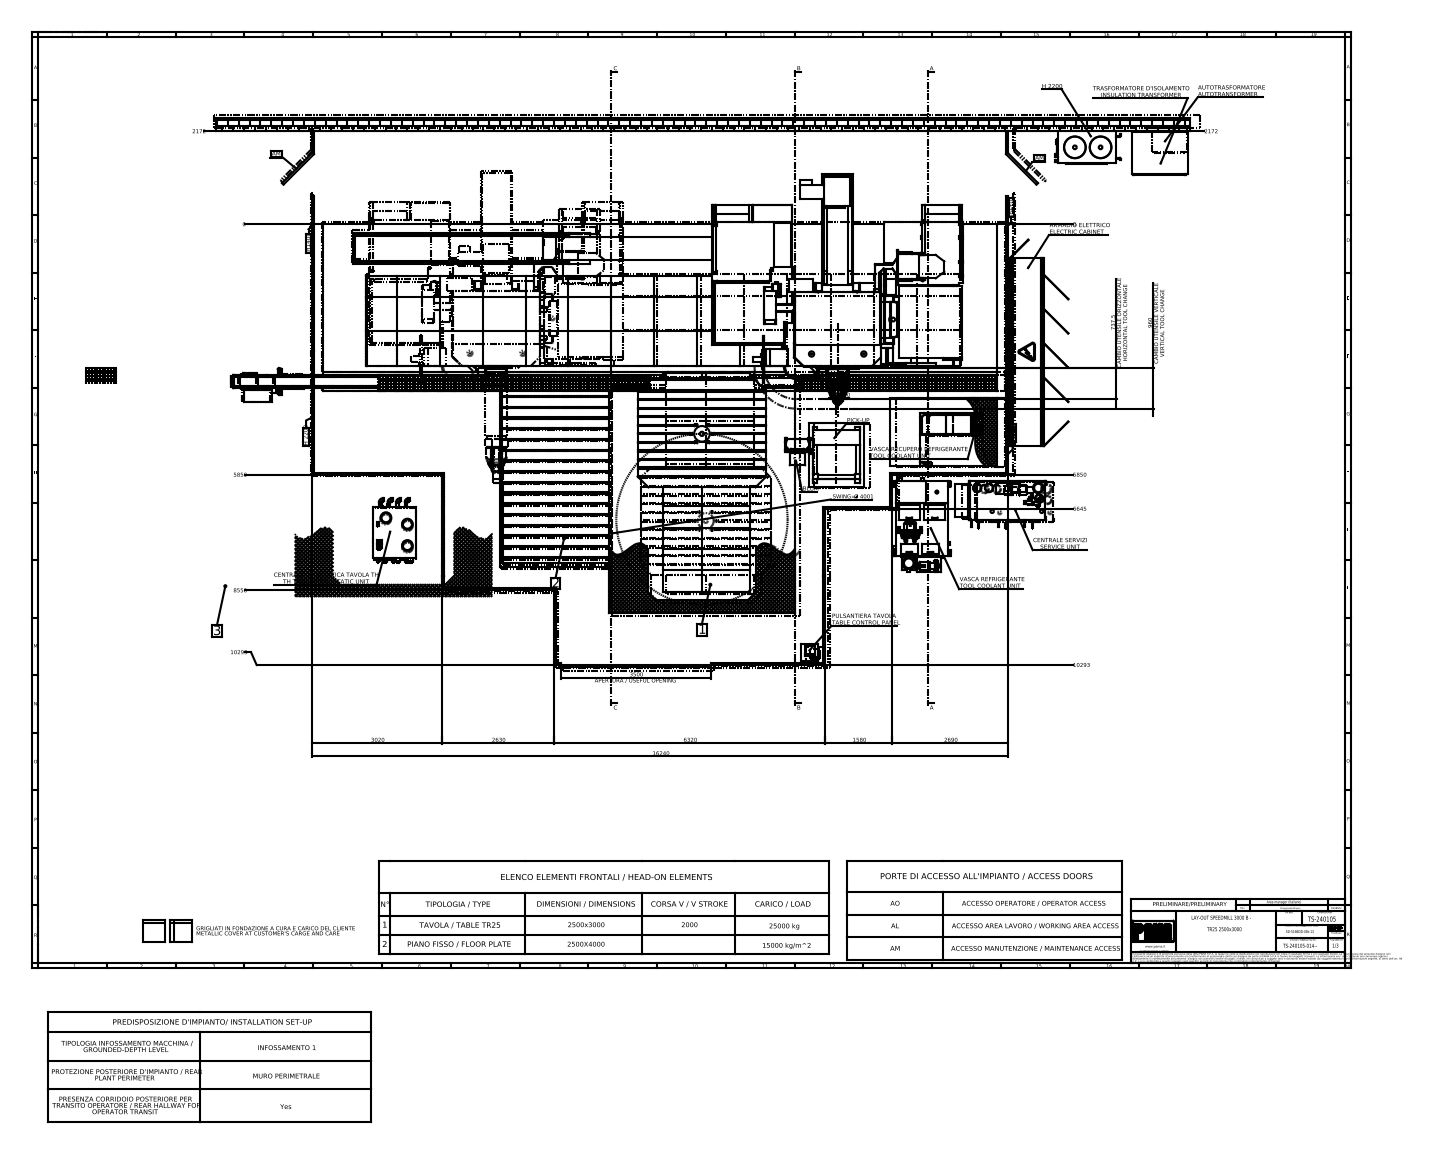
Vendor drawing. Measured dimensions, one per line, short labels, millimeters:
name: S003085_Lato TM - Inf. 1; S002839_PROLUNGA (L=300); S003495_Y=3500; S003389 (+8 more)
written by: SolidWorks 2023 (AUTOMOTIVE_DESIGN)
unit: mm
bodies: 566 solids, 8487 faces (6420 planar, 1656 cylindrical, 411 other)
size: 22740 × 15715 × 9400
volume: 753 200 000 000 mm³; area: 2 417 000 000 mm²
holes: 102× ⌀35, 63× ⌀69.6, 16× ⌀13, 8× ⌀14, 6× ⌀8, 6× ⌀32, 5× ⌀12, 4× ⌀6.8, 4× ⌀7, 4× ⌀12.5, 3× ⌀50, 3× ⌀56.66
bosses: 14× ⌀20, 10× ⌀9, 8× ⌀55, 8× ⌀30, 7× ⌀66.3, 7× ⌀60, 6× ⌀35, 5× ⌀200
rounds: 239× R5, 77× R10, 48× R15, 36× R6, 28× R2, 26× R35, 18× R8, 15× R20
face distances: 2000, 300, 50, 450, 1550, 15715, 15415, 22740, 100, 1950
hole spacings: 250, 500, 750, 1000, 1250, 1500, 1750, 2000
